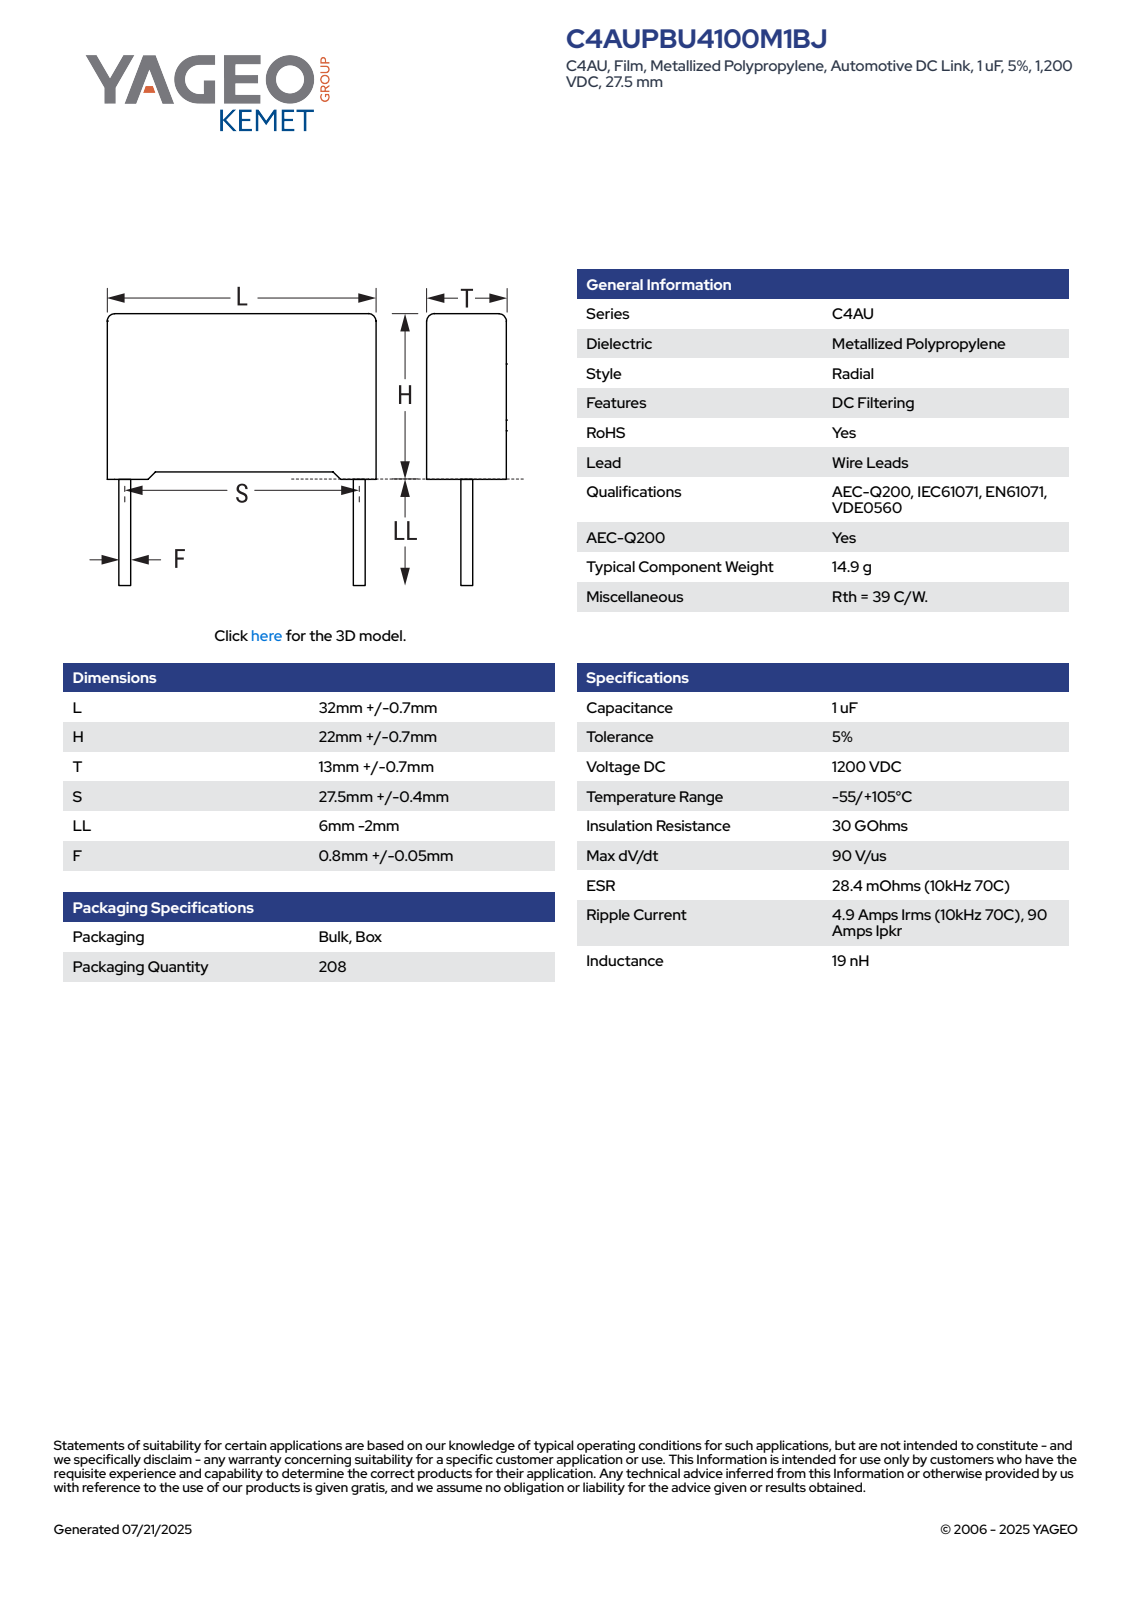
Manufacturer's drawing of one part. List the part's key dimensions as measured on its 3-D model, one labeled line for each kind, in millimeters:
Part name (STEP PRODUCT): CFP_RB4_32X22X13_L32.7H22.7T13.7S27.5S1LL4F0.85
STEP written by: SolidWorks 2021 (AUTOMOTIVE_DESIGN)
Units: millimetres
Bodies: 4 solids, 87 faces (79 planar, 8 cylindrical, 0 other)
Overall size (bounding box): 32.7 × 26.7 × 13.71
Volume: 9 911 mm³ · Surface area: 3 132 mm²
Round bosses / shafts (diameter × count): ⌀0.85 ×4
Main face-to-face distances: 13.7, 22.03, 32.7, 0.67, 22.7, 0.84, 12.86, 31.86, 12.02, 31.02
